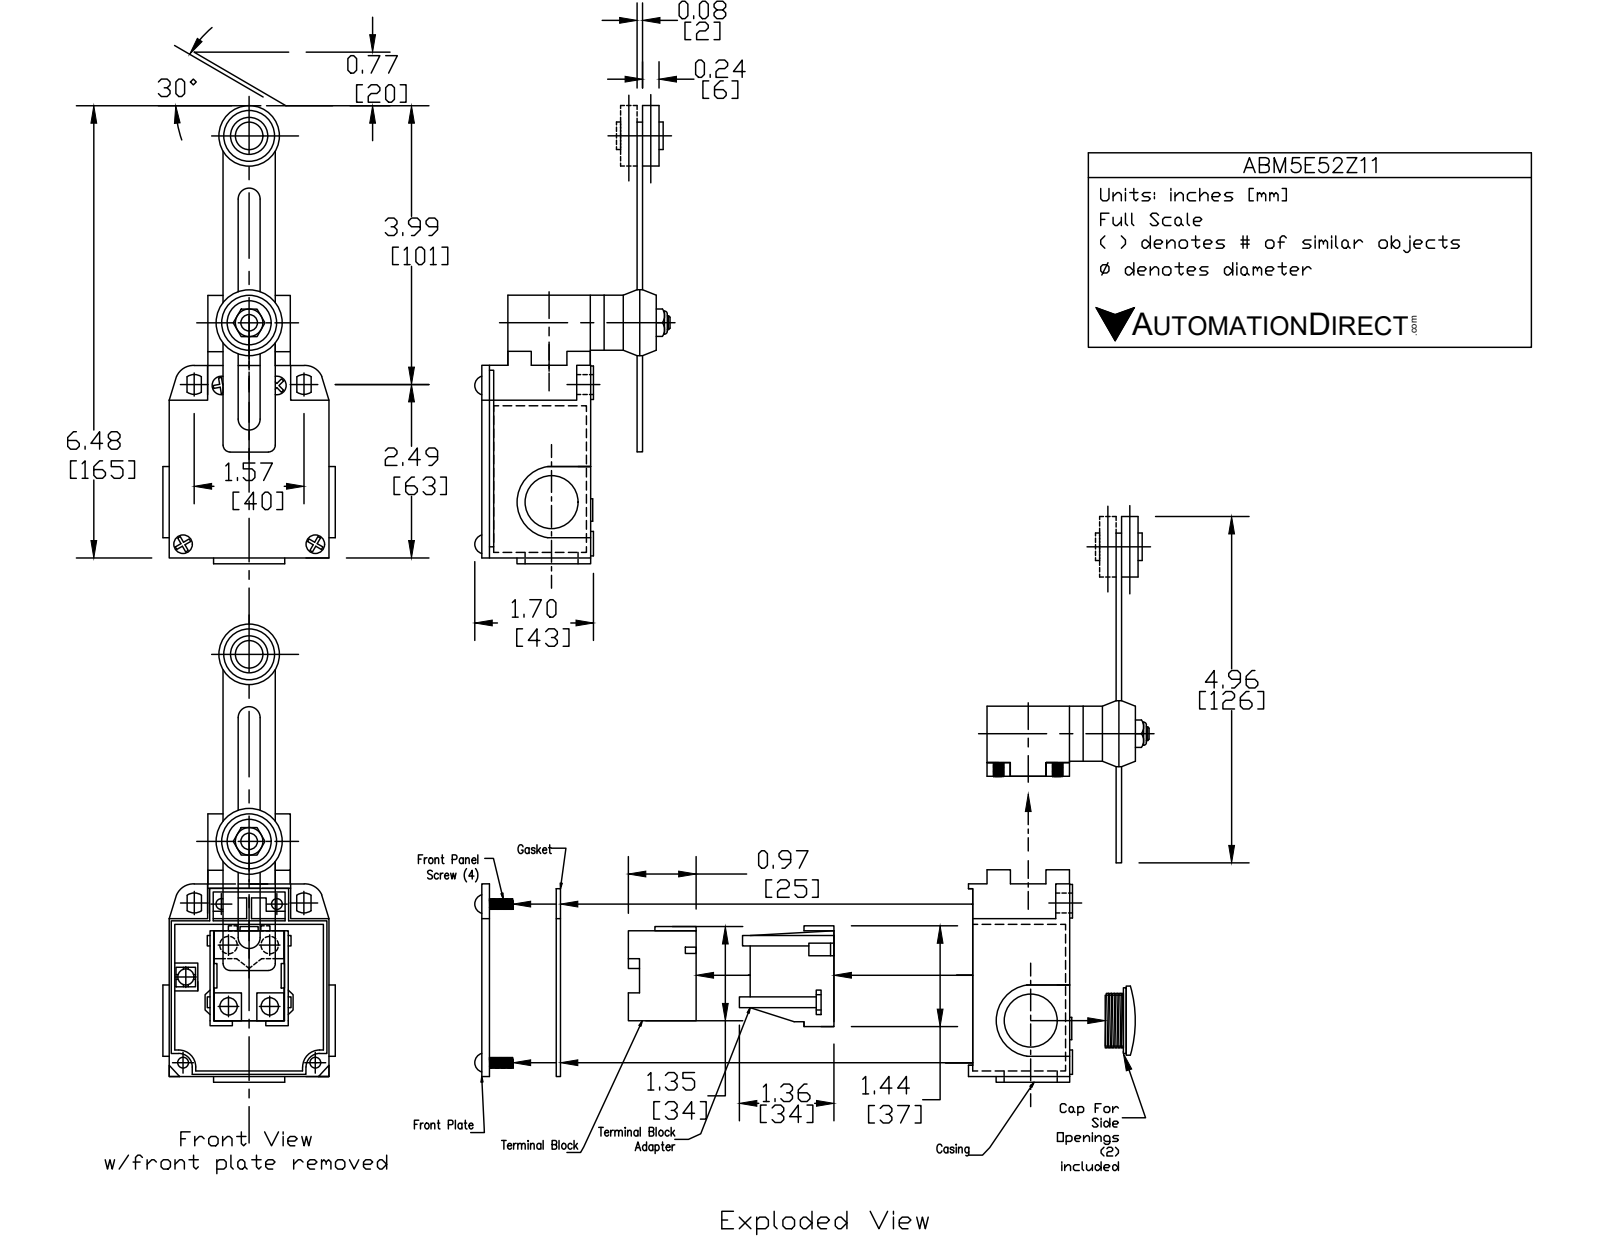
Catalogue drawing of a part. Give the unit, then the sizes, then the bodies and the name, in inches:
Units: inches
Overall size (bounding box): 6.535 × 2.35 × 1.575
Round holes (diameter × count): ⌀0.205 ×2, ⌀0.118 ×1, ⌀0.236 ×1, ⌀0.551 ×1, ⌀0.669 ×1, ⌀0.748 ×1
Round bosses / shafts (diameter × count): ⌀0.394 ×6, ⌀0.276 ×3, ⌀0.945 ×1, ⌀0.866 ×1, ⌀0.787 ×1, ⌀0.453 ×1, ⌀0.236 ×1
Partial cylindrical surfaces — rounded edges, fillets, slot ends (radius × count): R0.059 ×16, R0.039 ×4, R0.197 ×4, R0.118 ×2, R0.128 ×2, R0.159 ×2, R0.276 ×1, R0.453 ×1
Main face-to-face distances: 1.575, 1.555, 0.197, 1.181, 0.079, 0.323, 1.878, 0.402, 1.957, 1.378
Hole centre spacings: 0.551, 1.048, 2.641, 3.282
Volume: 8.878 in³ · Surface area: 51.08 in²
Bodies: 5 solids, 277 faces (131 planar, 109 cylindrical, 37 other)
Part name (STEP PRODUCT): ABM5E52Z11
STEP written by: SolidWorks 2017 (AUTOMOTIVE_DESIGN)
